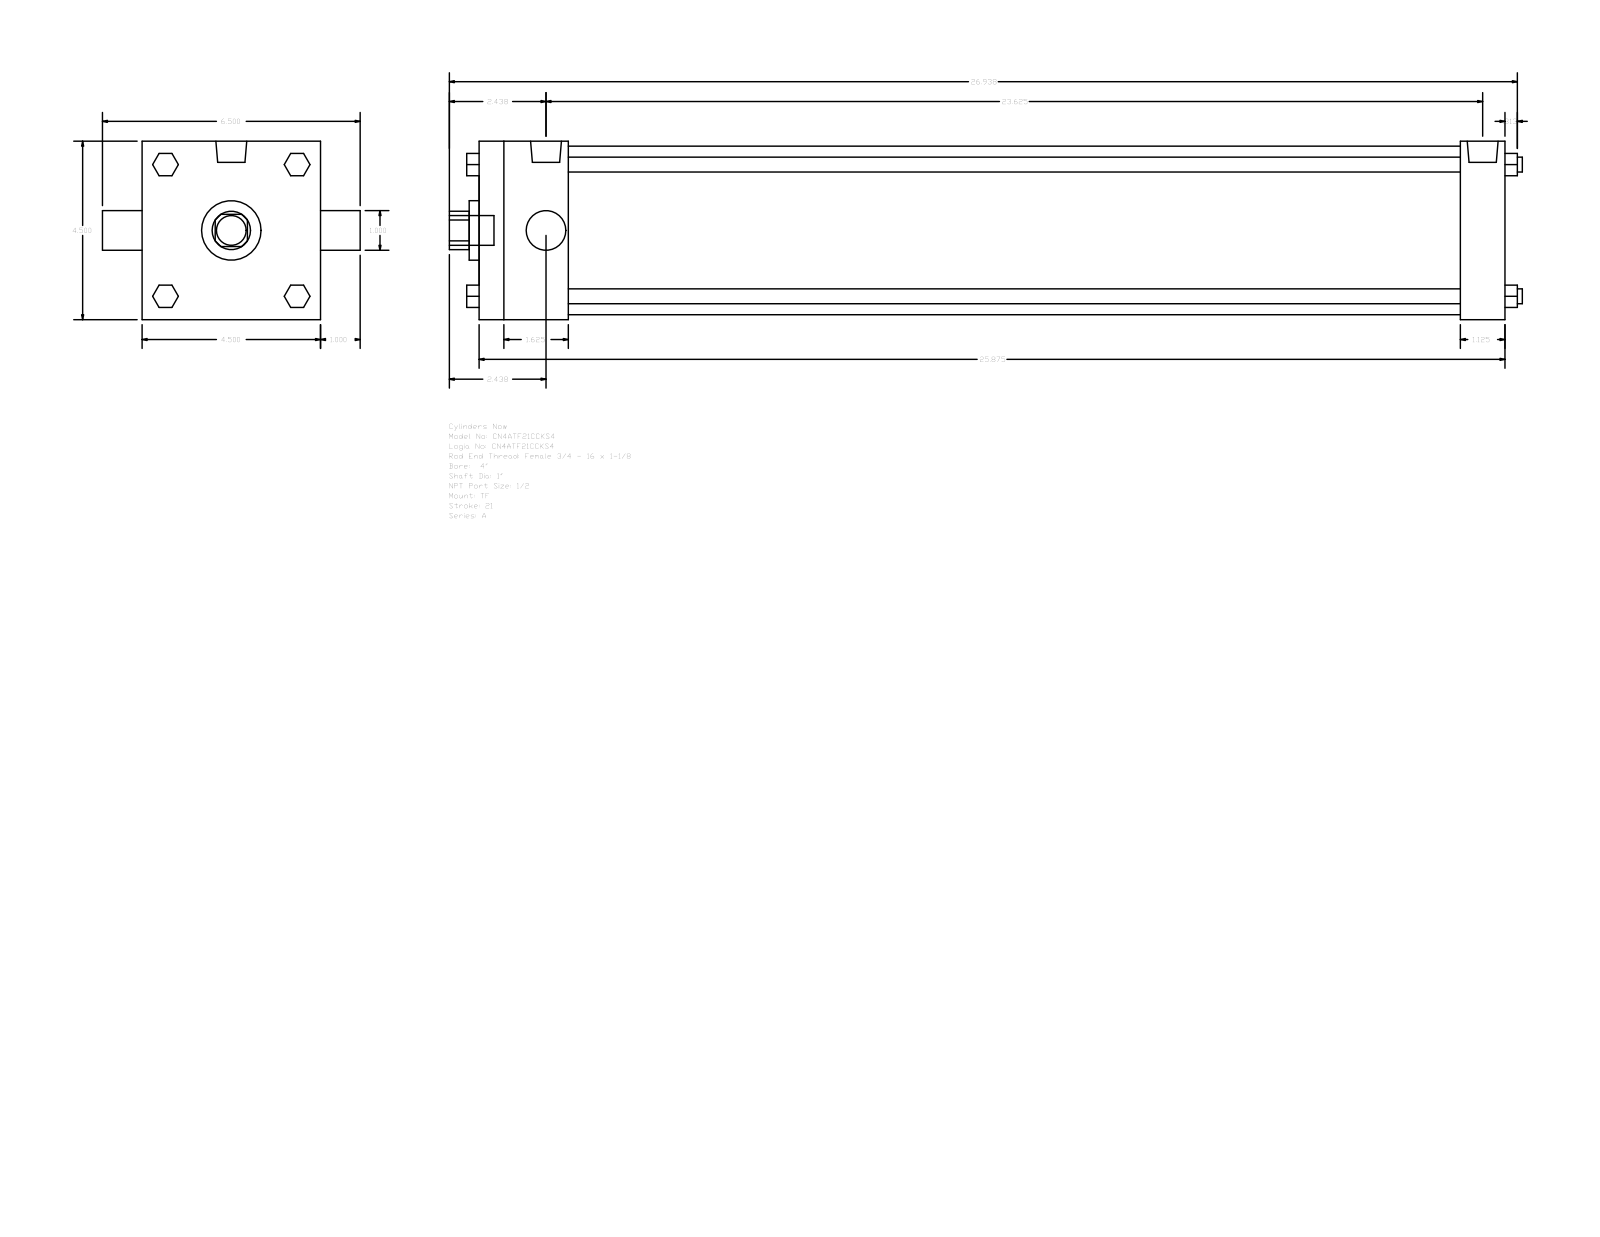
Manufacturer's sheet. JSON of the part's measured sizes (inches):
{"part_name": "A_TF__0400_1", "step_written_by": "GSSL Pune (CONFIG_CONTROL_DESIGN)", "units": "inches", "bodies": {"solids": 0, "faces": 120, "planar": 92, "cylindrical": 28, "other": 0}, "overall_size": [27.063, 6.5, 4.5], "round_holes": [[1, 2], [1.5, 1], [4.25, 1]], "round_bosses_or_shafts": [[0.375, 4], [0.344, 3], [0.778, 2], [0.75, 1]], "partial_cylinders_radius": [[0.484, 1]], "face_to_face_distances": [4.5, 25.875, 1.125, 24.75, 2.25, 22.5, 23.625, 0.563, 1.66, 2.875]}
